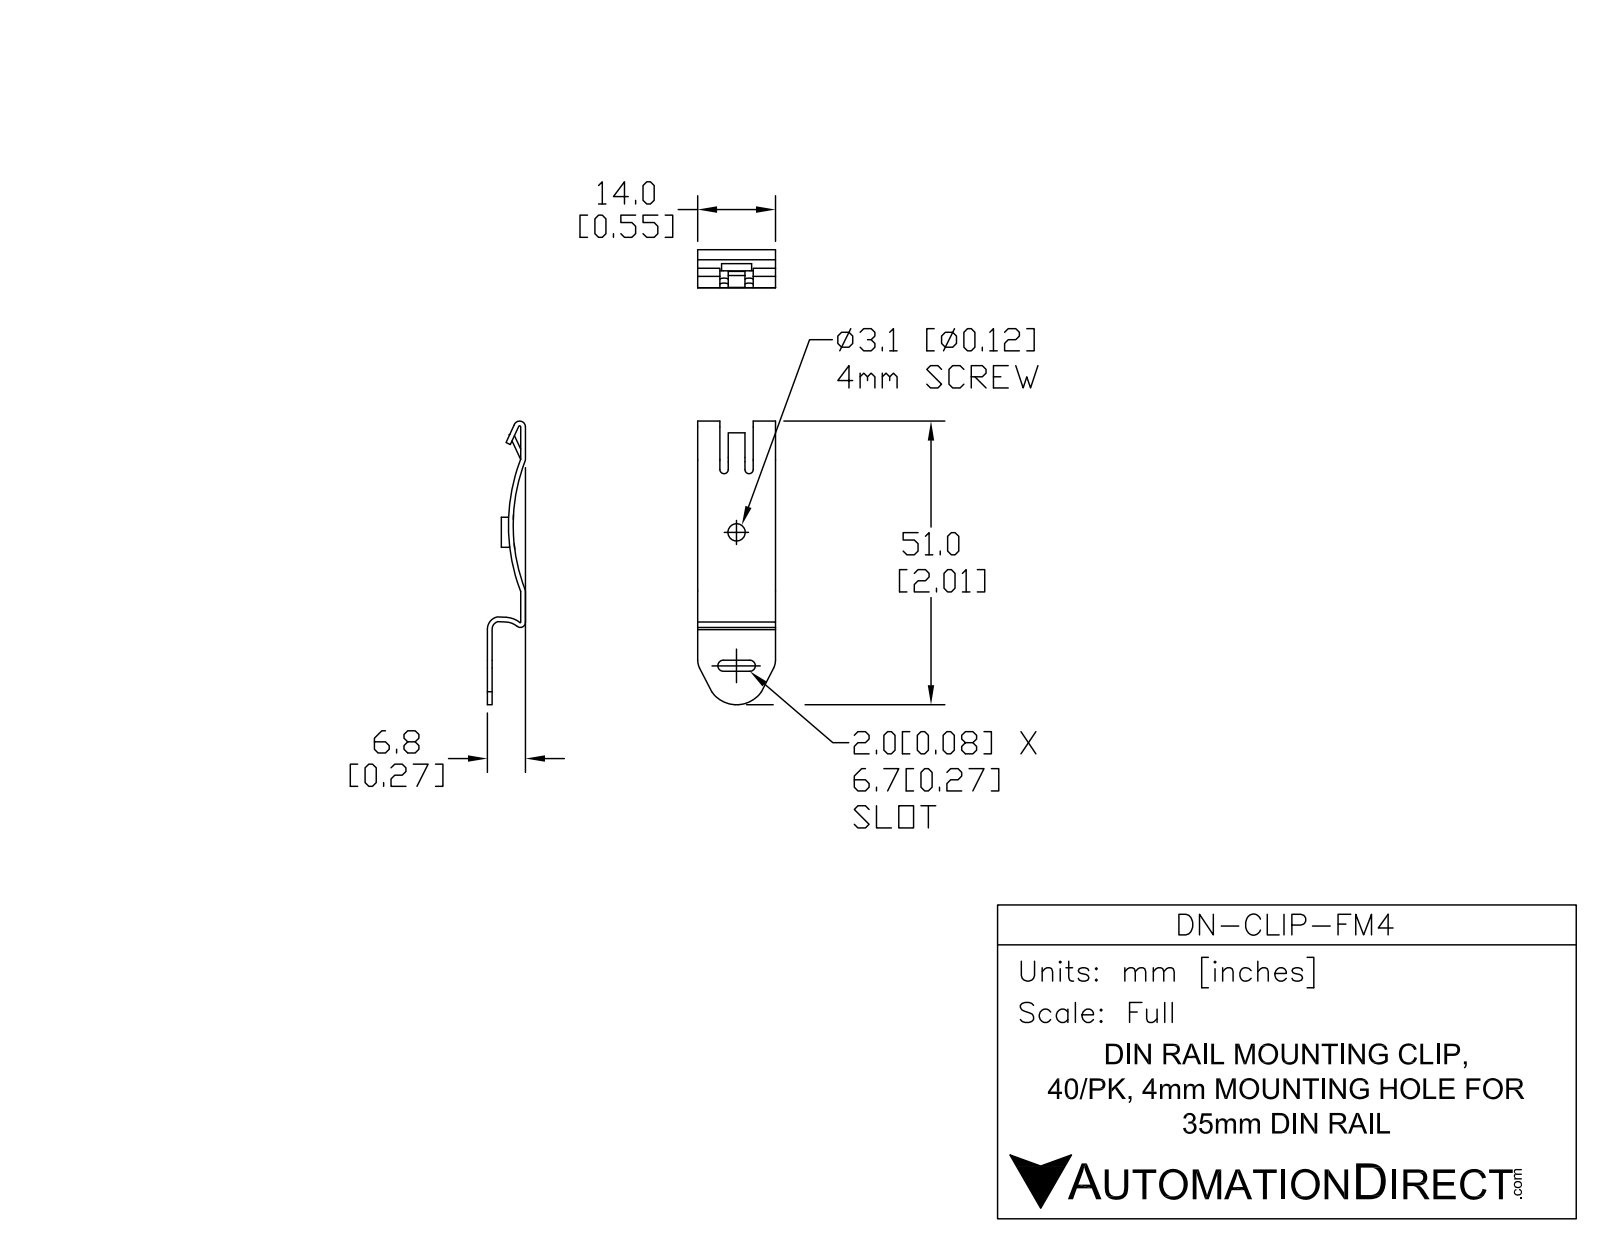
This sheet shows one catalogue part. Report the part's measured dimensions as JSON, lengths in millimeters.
{"part_name": "DN-CLIP-FM4", "step_written_by": "SolidWorks 2011 (AUTOMOTIVE_DESIGN)", "units": "millimeters", "bodies": {"solids": 1, "faces": 61, "planar": 33, "cylindrical": 27, "other": 1}, "overall_size": [51, 14, 6.85], "volume_mm3": 653, "surface_area_mm2": 1736, "round_holes": [[4.35, 1]], "round_bosses_or_shafts": [[5.42, 1]], "partial_cylinders_radius": [[1, 3], [0.75, 2], [0.75, 2], [3, 2], [0.2, 1], [0.93, 1], [1.04, 1], [1.41, 1]], "face_to_face_distances": [0.85, 6, 6.85, 5.15, 14, 4, 10, 0.8, 1.5, 5.5]}
